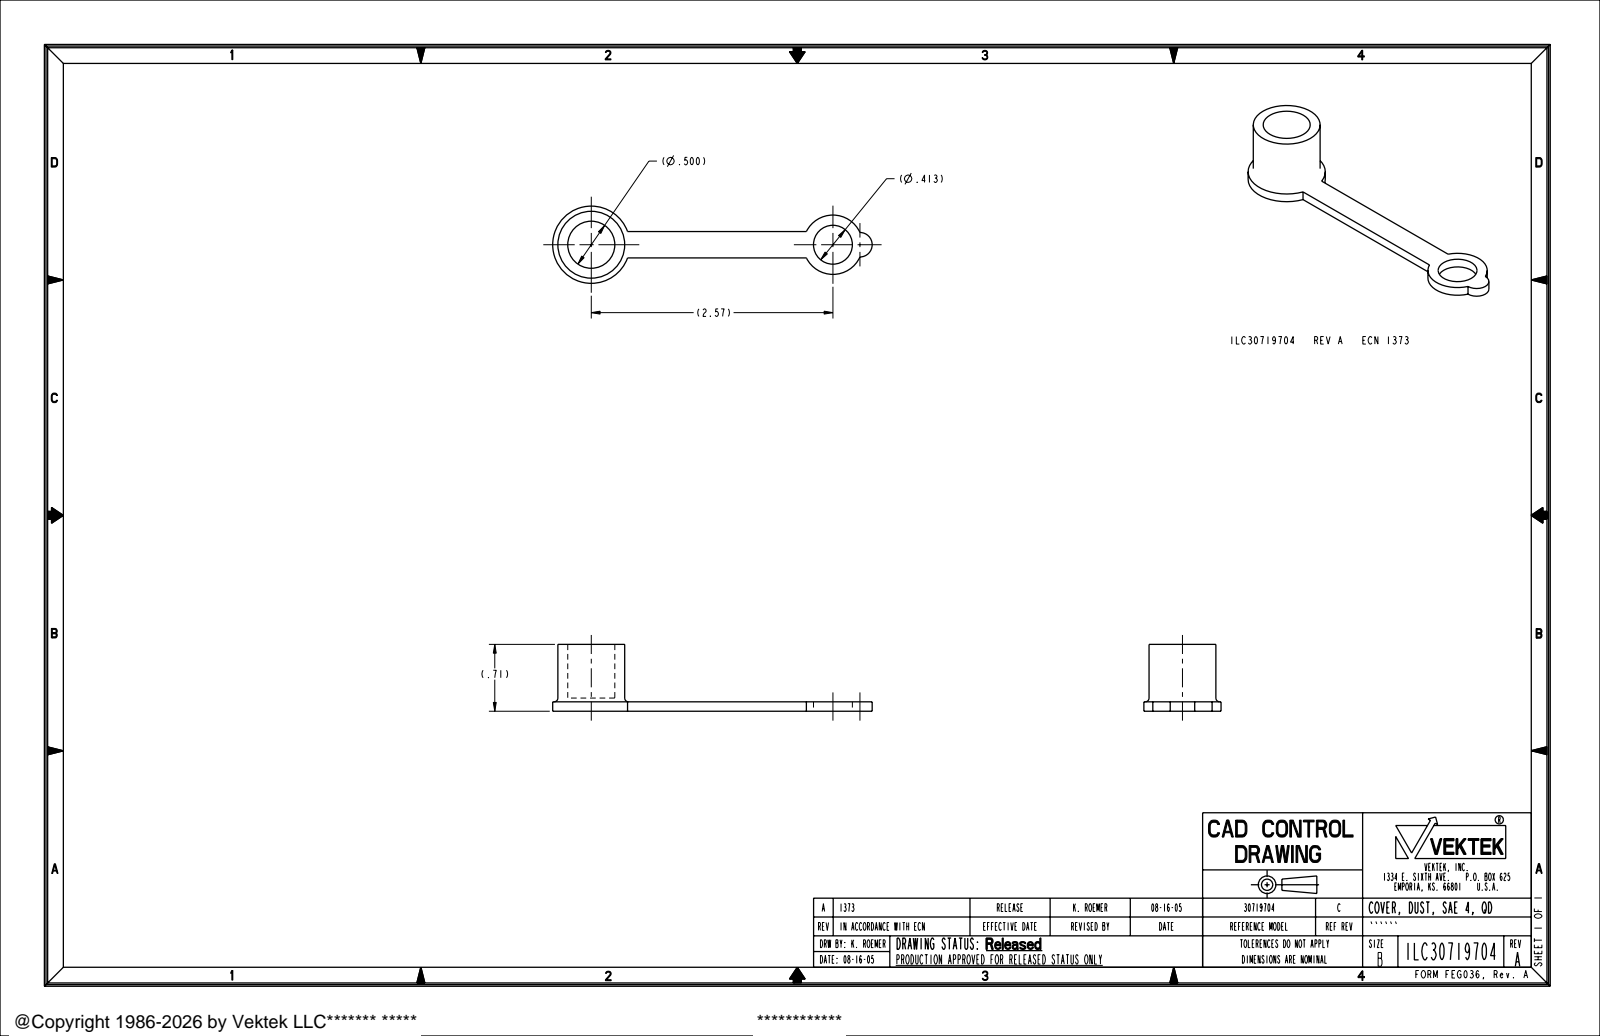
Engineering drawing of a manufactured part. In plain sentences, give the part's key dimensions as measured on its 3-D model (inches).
The part is named "ILC30719704". Its 3-D file was written by "PRO/ENGINEER BY PARAMETRIC TECHNOLOGY CORPORATION, 2004290 (AUTOMOTIVE_DESIGN_CC2)". It is 1 solid with 18 faces: 6 planar, 10 cylindrical and 2 other. Overall it measures 3.394 by 0.82 by 0.71 inches. Its volume is 0.255 cubic inches and its surface area 5.637 square inches. Round holes: 1 of diameter 0.413, 1 of diameter 0.5. Round bosses or shafts: 1 of diameter 0.82, 1 of diameter 0.71. Partial cylindrical surfaces (rounded edges, fillets, slot ends): 1 of radius 0.13, 1 of radius 0.315. The main face-to-face distances are 0.1, 0.71, 0.61, 0.14, 0.04, 0.57, 0.28. The hole center spacings are 2.568.
